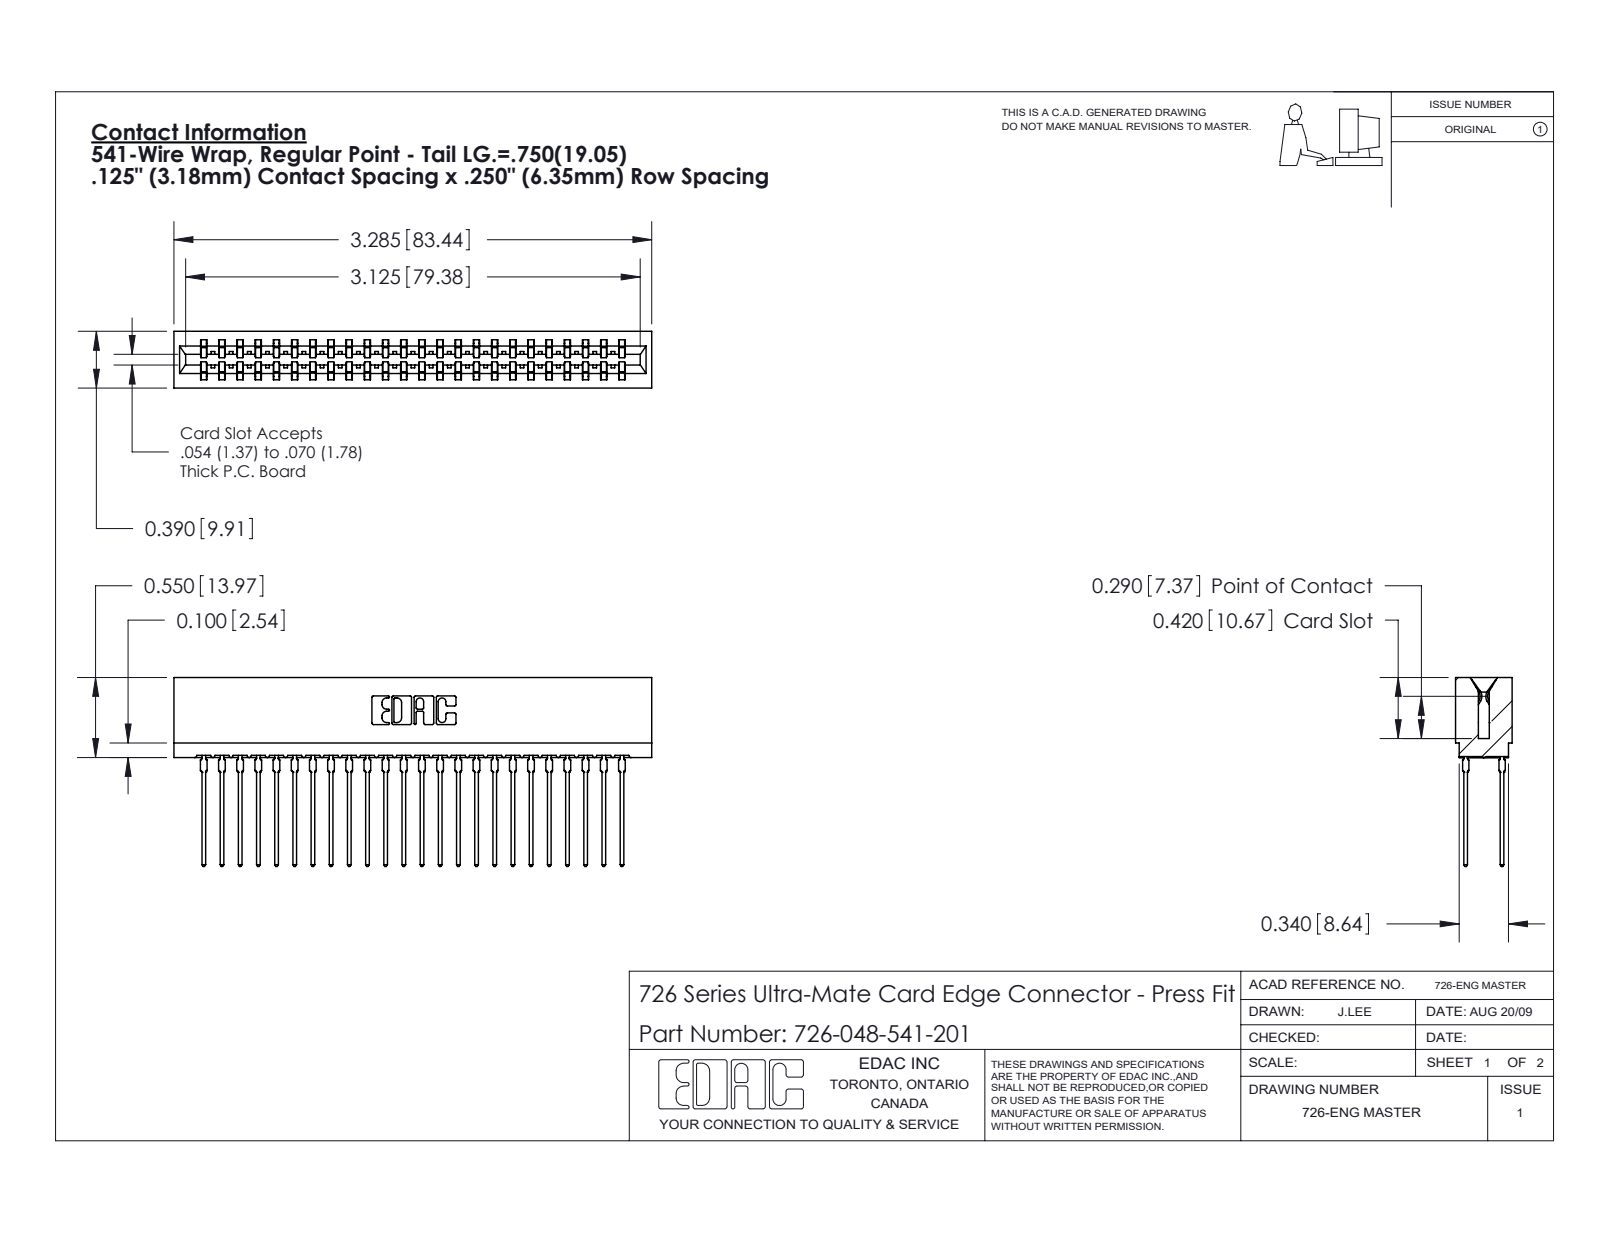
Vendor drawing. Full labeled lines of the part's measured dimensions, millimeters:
Part name (STEP PRODUCT): 726 Part_.515 Slot Depth - 01; 726-048-541-201; 746-292-001_541
STEP written by: SolidWorks 2020 (CONFIG_CONTROL_DESIGN)
Units: millimetres
Bodies: 49 solids, 4393 faces (2263 planar, 882 cylindrical, 1248 other)
Overall size (bounding box): 83.4 × 33 × 9.9
Volume: 8 030 mm³ · Surface area: 14 300 mm²
Partial cylindrical surfaces — rounded edges, fillets, slot ends (radius × count): R0.5 ×96, R0.4 ×25, R0.3 ×22, R0.1 ×8, R0.3 ×8, R0.2 ×6, R0.8 ×6, R0.7 ×3
Main face-to-face distances: 1.4, 8.5, 0.6, 6.4, 7.8, 2.1, 9.9, 7, 1.1, 19.1
